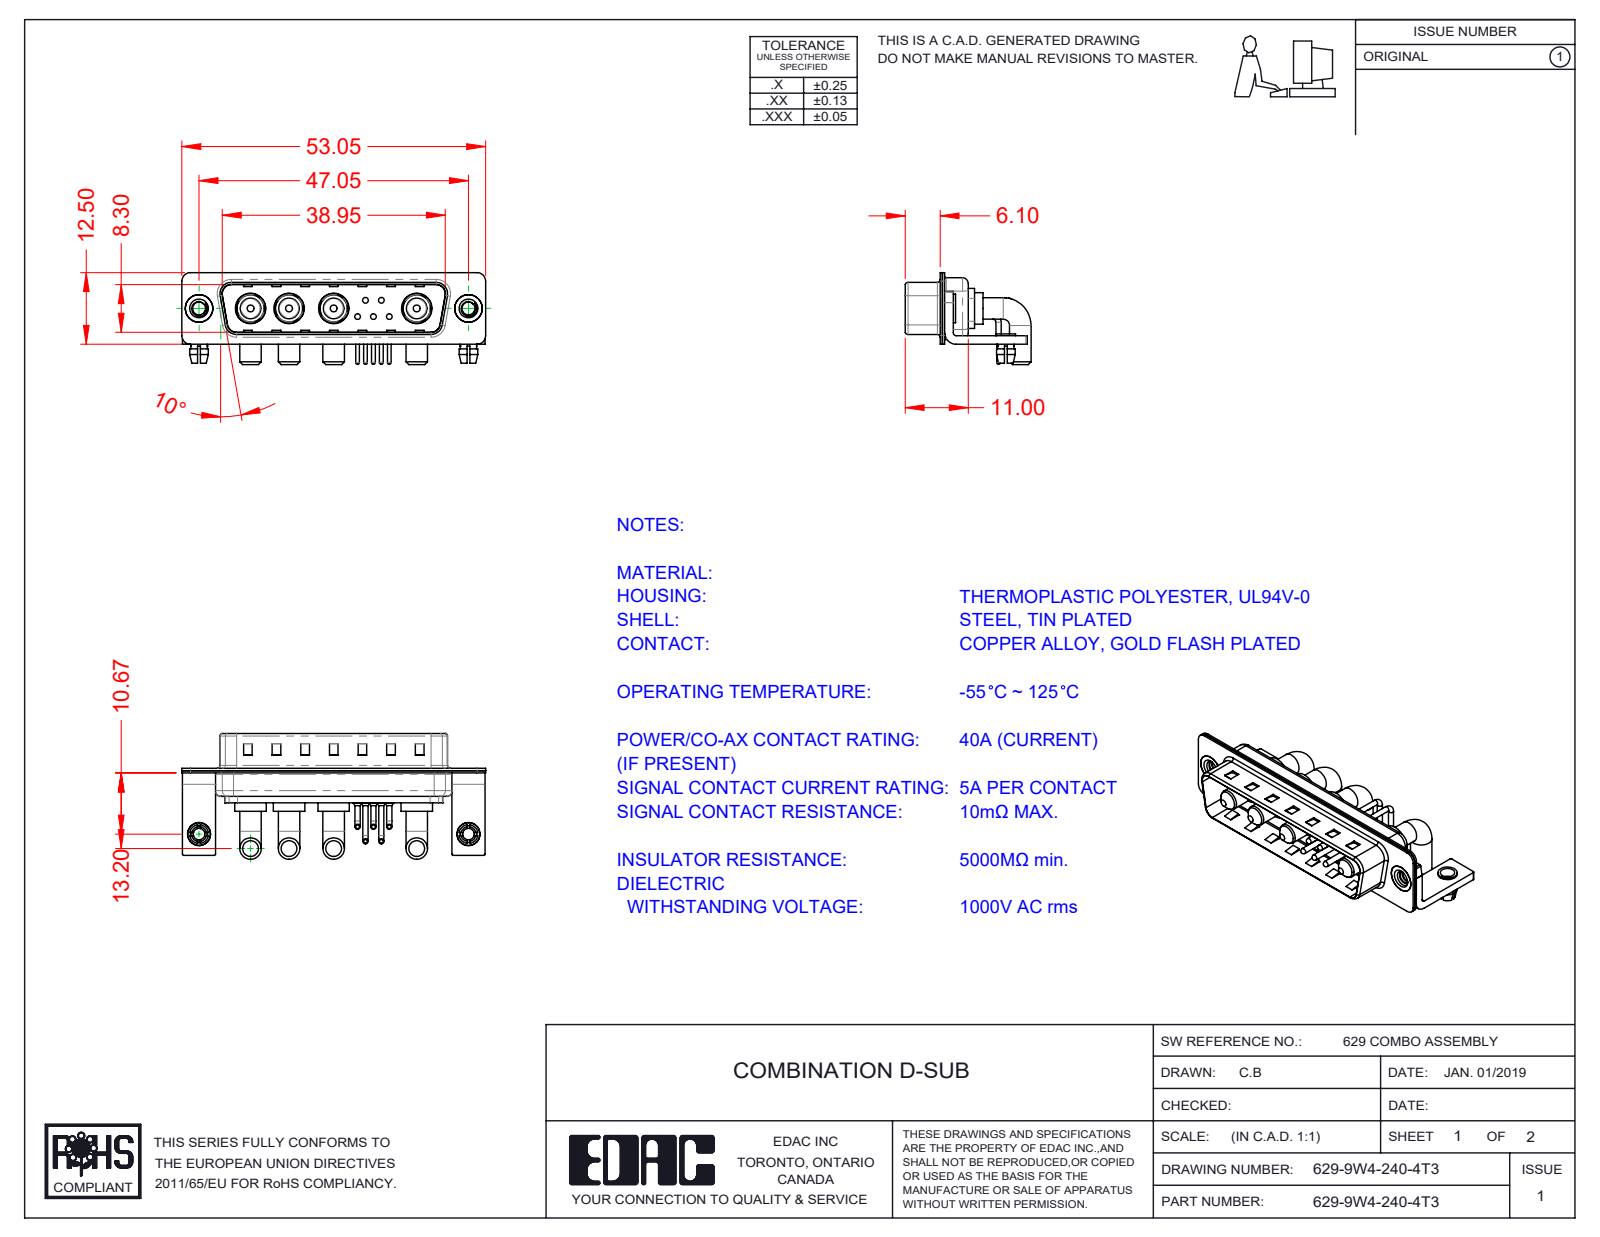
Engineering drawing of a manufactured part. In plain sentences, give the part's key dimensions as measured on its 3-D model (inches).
The part is named "629Combo Shell Rear_25 Contacts; 629Combo Contact Row 1; 629Combo Board Lock; 629Combo Threaded Rivet_3 (+6 more)". Its 3-D file was written by "SolidWorks 2020 (CONFIG_CONTROL_DESIGN)". It is 22 solids with 1230 faces: 599 planar, 451 cylindrical and 180 other. Overall it measures 2.089 by 0.865 by 0.632 inches. Its volume is 0.238 cubic inches and its surface area 12.75 square inches. Round holes: 7 of diameter 0.079, 5 of diameter 0.03, 5 of diameter 0.063, 4 of diameter 0.191, 4 of diameter 0.209, 2 of diameter 0.089, 2 of diameter 0.098, 2 of diameter 0.126, 2 of diameter 0.157, 2 of diameter 0.189. Round bosses or shafts: 10 of diameter 0.035, 8 of diameter 0.148, 5 of diameter 0.059, 5 of diameter 0.039, 5 of diameter 0.026, 4 of diameter 0.217, 4 of diameter 0.205, 4 of diameter 0.187. Partial cylindrical surfaces (rounded edges, fillets, slot ends): 16 of radius 0.01, 16 of radius 0.059, 13 of radius 0.079, 9 of radius 0.02, 8 of radius 0.063, 5 of radius 0.04, 4 of radius 0.024, 4 of radius 0.026. The main face-to-face distances are 0.016, 0.031, 0.374, 0.059, 0.358, 0.343, 0.39, 0.205, 0.03, 0.047. The hole center spacings are 0.124, 0.109, 0.198, 0.571, 1.852, 0.109, 0.173, 0.174.
